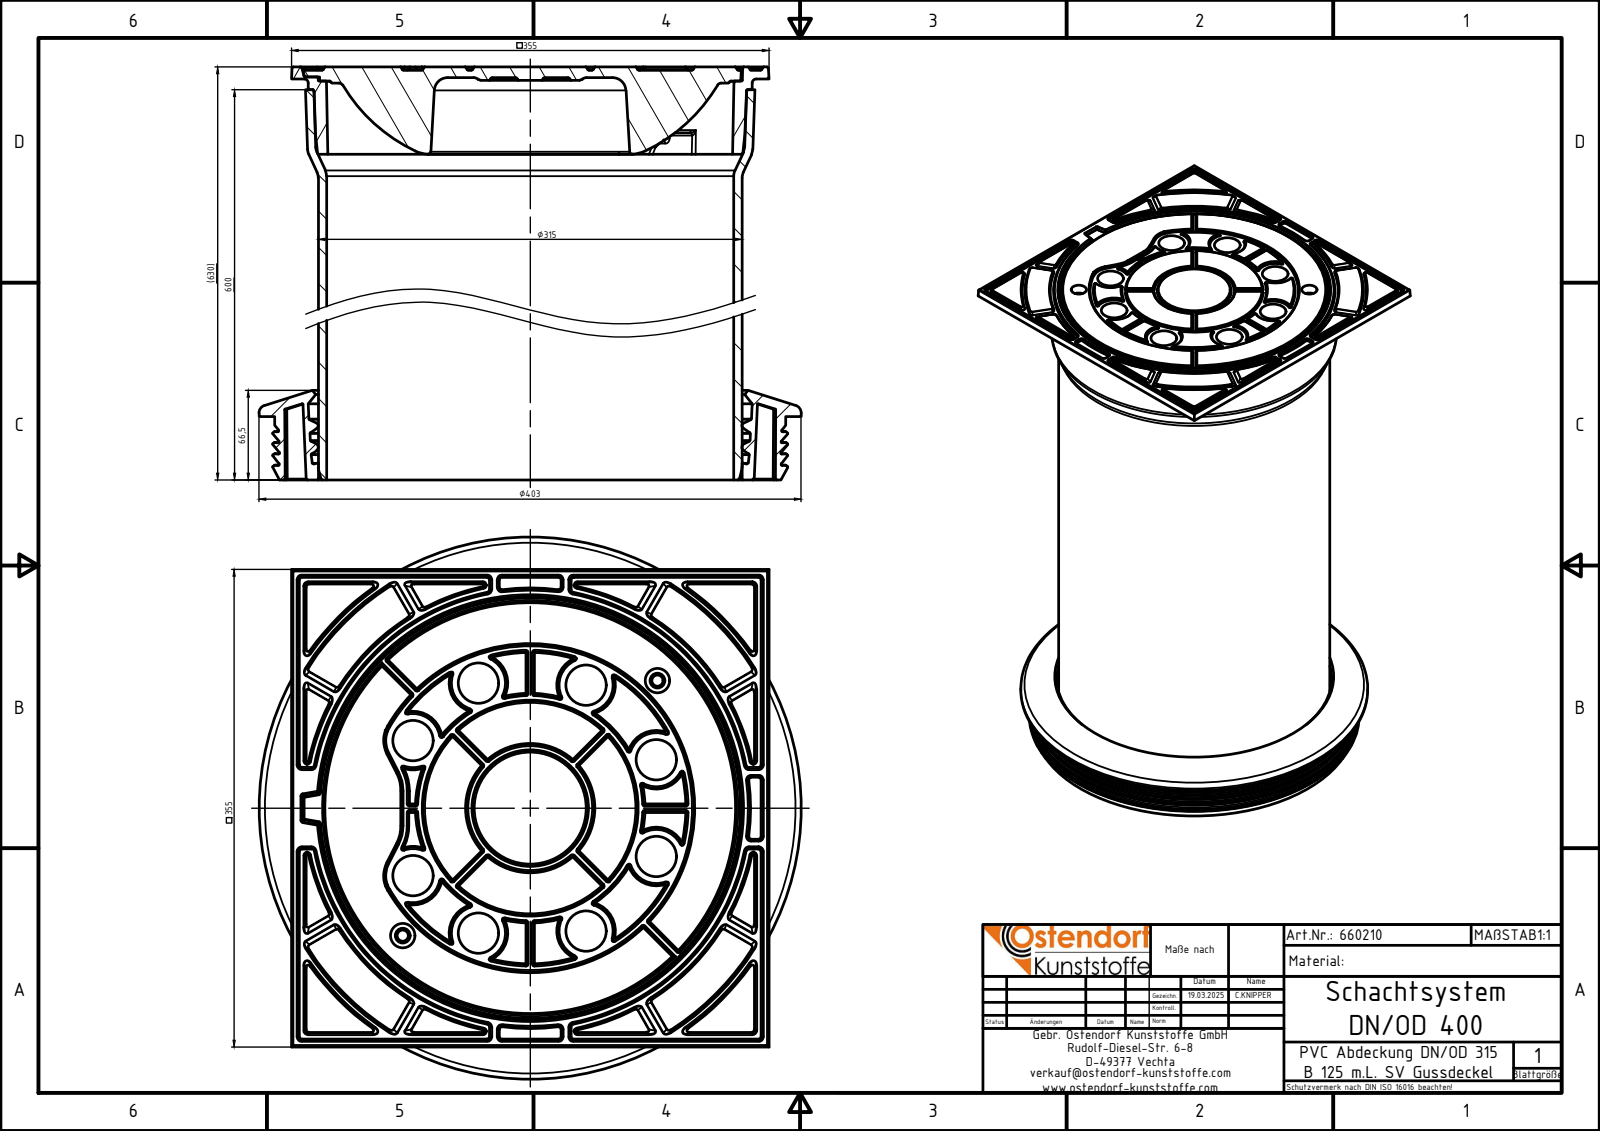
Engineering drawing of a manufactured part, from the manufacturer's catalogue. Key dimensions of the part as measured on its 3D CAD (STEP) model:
Part name (STEP PRODUCT): 660210z; 660205_Dichtungz; 660205_geändertz; 990000z (+2 more)
STEP written by: Autodesk Inventor 2024 (AUTOMOTIVE_DESIGN)
Units: millimetres
Bodies: 4 solids, 1528 faces (200 planar, 257 cylindrical, 1071 other)
Overall size (bounding box): 617 × 403 × 403
Volume: 7 841 000 mm³ · Surface area: 2 067 000 mm²
Round holes (diameter × count): ⌀30 ×8, ⌀8.38 ×2, ⌀11 ×2, ⌀18 ×2, ⌀302.6 ×1, ⌀315 ×1
Round bosses / shafts (diameter × count): ⌀403 ×1, ⌀380 ×1, ⌀330 ×1
Partial cylindrical surfaces — rounded edges, fillets, slot ends (radius × count): R1 ×161, R2 ×8, R2.5 ×8
Main face-to-face distances: 9, 8, 2.5, 6.5, 608, 614.5, 617, 1.5, 47, 561
Hole centre spacings: 100.5, 64.61, 76.11, 80.14, 134, 135.14, 143.97, 151.12
